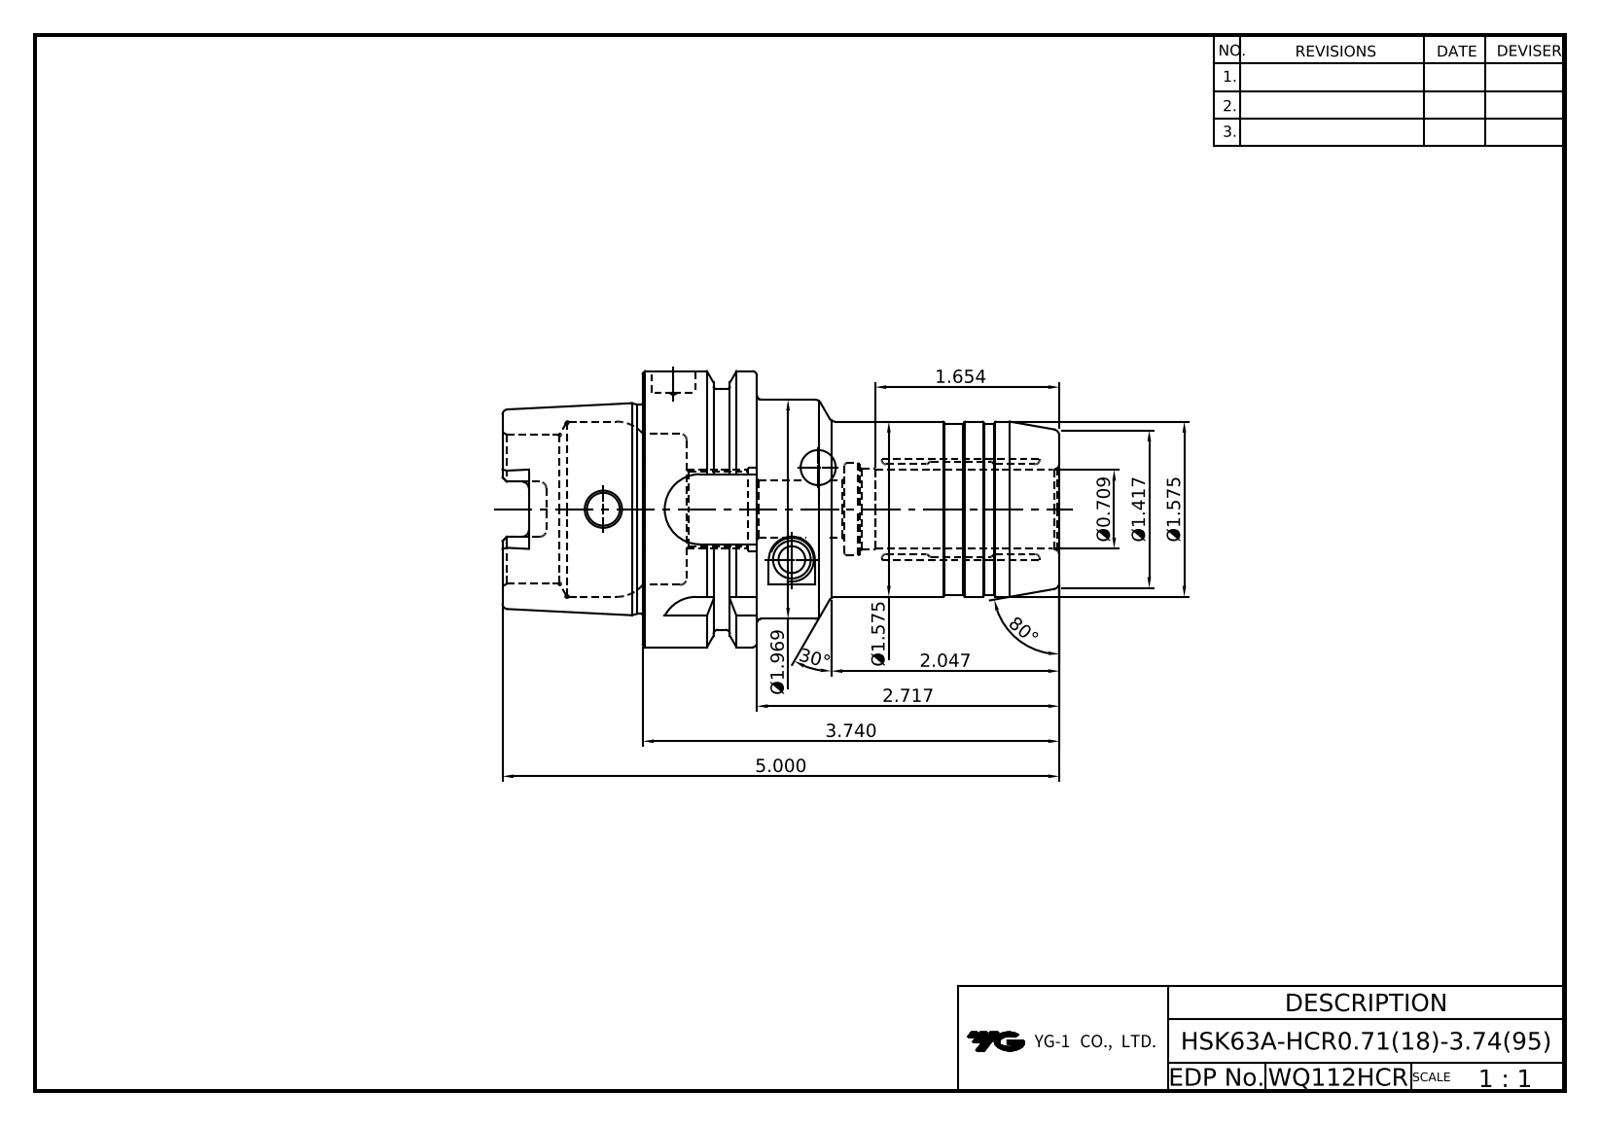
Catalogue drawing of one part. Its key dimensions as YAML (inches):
part_name: "LO-HSK63A-HCR18-95"
step_written_by: "Autodesk Inventor 2020 (AUTOMOTIVE_DESIGN)"
units: inches
bodies: {solids: 1, faces: 135, planar: 42, cylindrical: 38, other: 55}
overall_size: [5, 2.48, 2.48]
volume: 9.864
surface_area: 53.21
round_holes:
  - {diameter: 0.295, count: 1}
  - {diameter: 0.394, count: 1}
  - {diameter: 0.52, count: 1}
  - {diameter: 0.666, count: 1}
  - {diameter: 0.709, count: 1}
  - {diameter: 0.724, count: 1}
  - {diameter: 0.748, count: 1}
  - {diameter: 1.339, count: 1}
round_bosses_or_shafts:
  - {diameter: 2.48, count: 1}
  - {diameter: 2.165, count: 1}
  - {diameter: 1.969, count: 1}
  - {diameter: 1.891, count: 1}
  - {diameter: 1.575, count: 1}
  - {diameter: 1.535, count: 1}
partial_cylinders:
  - {radius: 0.059, count: 6}
  - {radius: 0.113, count: 4}
  - {radius: 0.315, count: 4}
face_to_face_distances: [1.024, 2.717, 3.74, 0.394, 0.63, 3.346, 1.26, 1.654, 2.283, 5]
